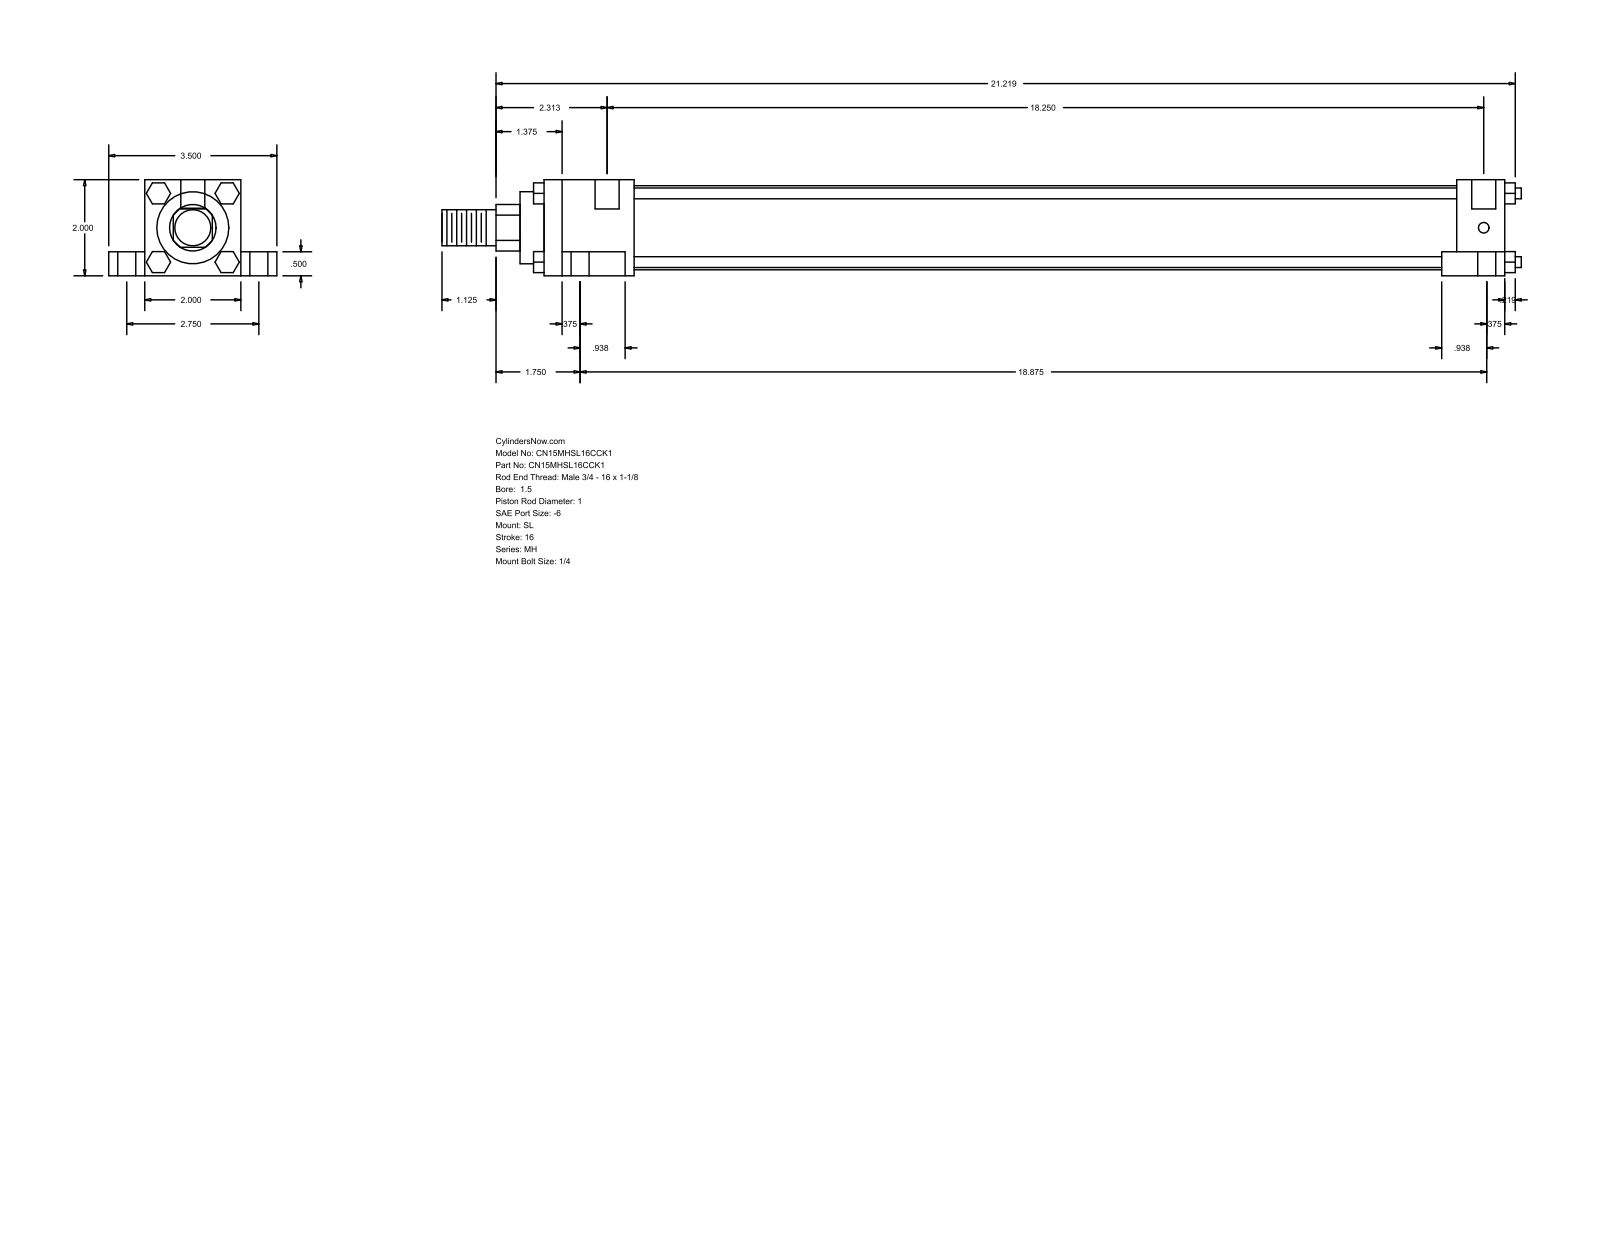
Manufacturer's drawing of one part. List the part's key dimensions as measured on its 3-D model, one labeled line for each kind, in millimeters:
Part name (STEP PRODUCT): MH_SL__0150_1
STEP written by: GSSL Pune (CONFIG_CONTROL_DESIGN)
Units: millimetres
Bodies: 0 solids, 148 faces (112 planar, 36 cylindrical, 0 other)
Overall size (bounding box): 570.71 × 88.9 × 50.8
Round holes (diameter × count): ⌀5.56 ×4, ⌀9.53 ×4, ⌀15.88 ×4, ⌀12.7 ×2
Round bosses / shafts (diameter × count): ⌀5.71 ×4, ⌀44.45 ×1, ⌀38.1 ×1, ⌀25.4 ×1, ⌀19.05 ×1
Partial cylindrical surfaces — rounded edges, fillets, slot ends (radius × count): R12.29 ×1
Main face-to-face distances: 50.8, 12.7, 38.1, 19.05, 69.85, 508, 25.4, 9.52, 33.34, 465.14
Hole centre spacings: 34.96, 36.64, 37.73, 69.84, 466.45, 466.73, 469.62, 479.11
